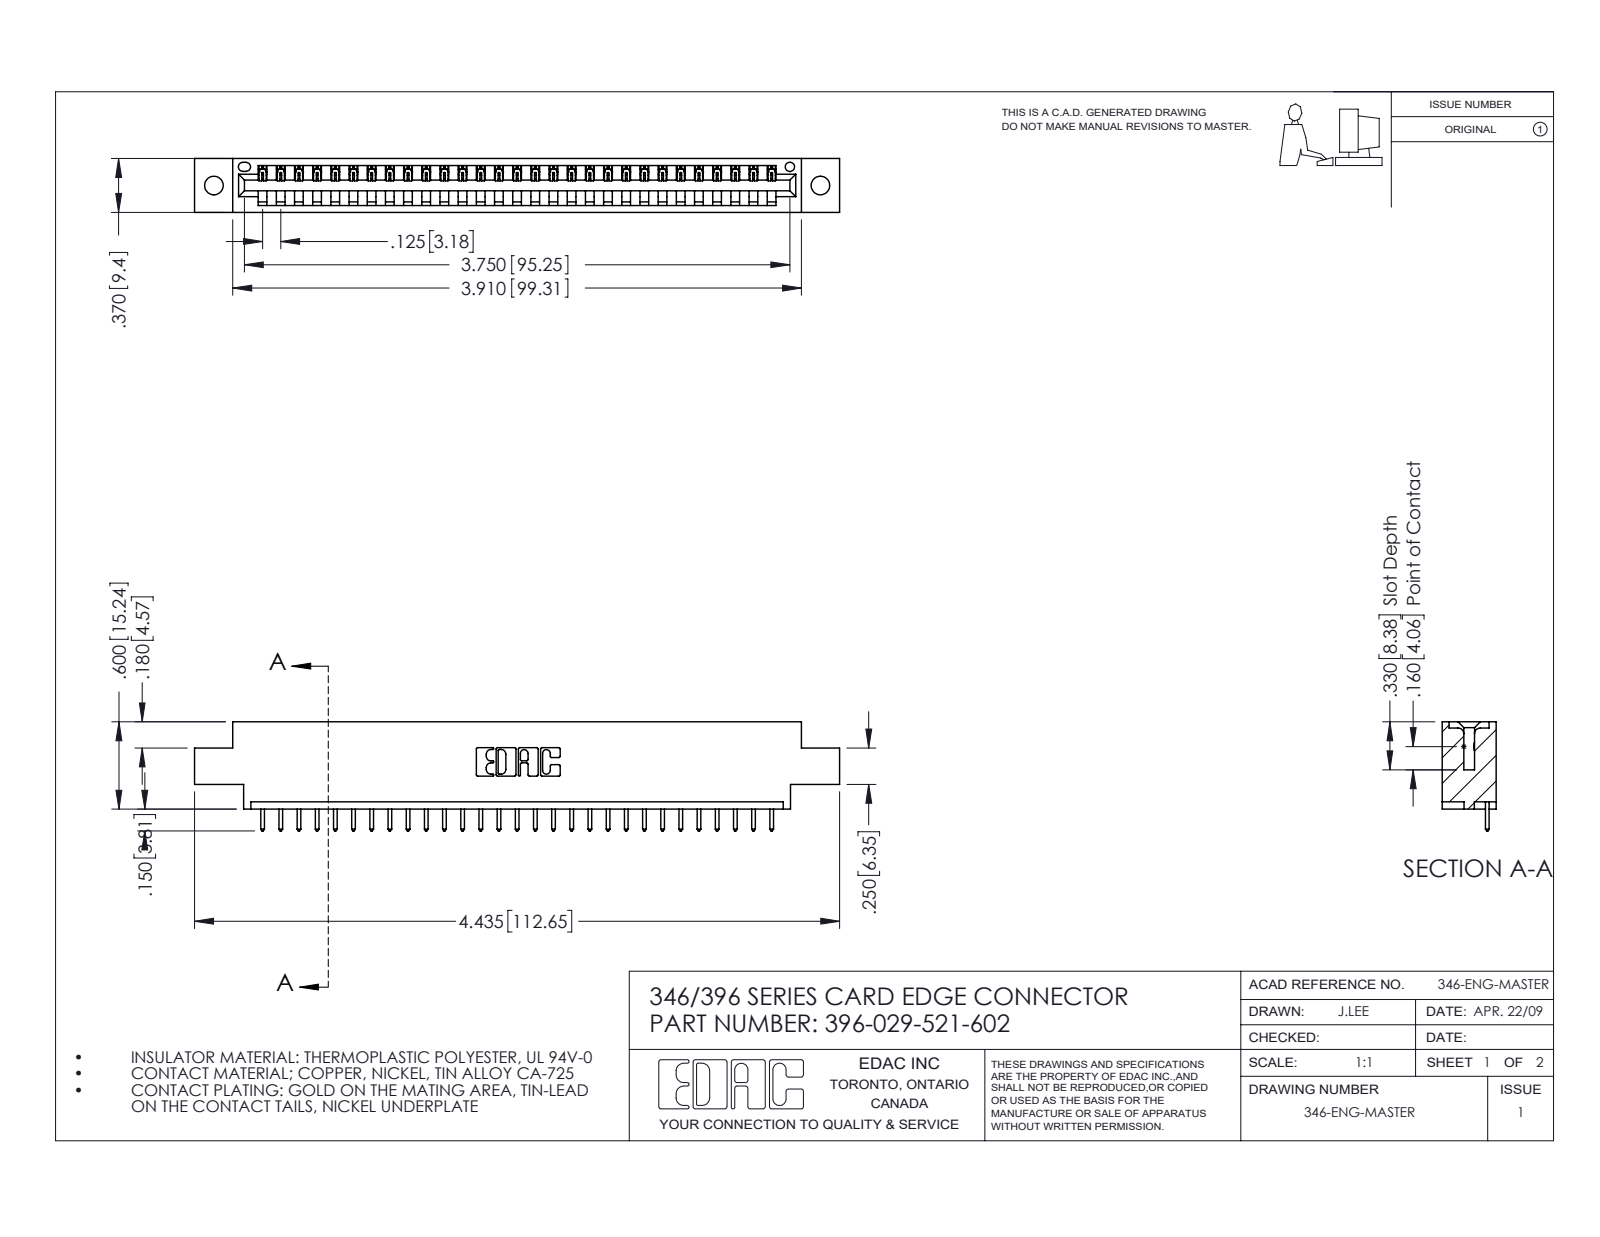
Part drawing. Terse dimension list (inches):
name: 345-292-001_345-293-121; 396-029-521-602; 346 Part_0.170 Offset - 0.128 Dia
written by: SolidWorks 2016 (CONFIG_CONTROL_DESIGN)
unit: in
bodies: 30 solids, 1808 faces (1240 planar, 568 cylindrical, 0 other)
size: 4.435 × 0.75 × 0.37
volume: 0.636 in³; area: 19.29 in²
holes: 2× ⌀0.128, 1× ⌀0.064
rounds: 58× R0.006, 58× R0.01, 22× R0.01, 6× R0.007, 6× R0.031, 3× R0.026, 2× R0.031, 2× R0.04
face distances: 0.048, 0.322, 0.37, 0.25, 0.072, 0.298, 0.025, 0.148, 0.222, 0.1
hole spacings: 0.246, 3.962, 4.17
